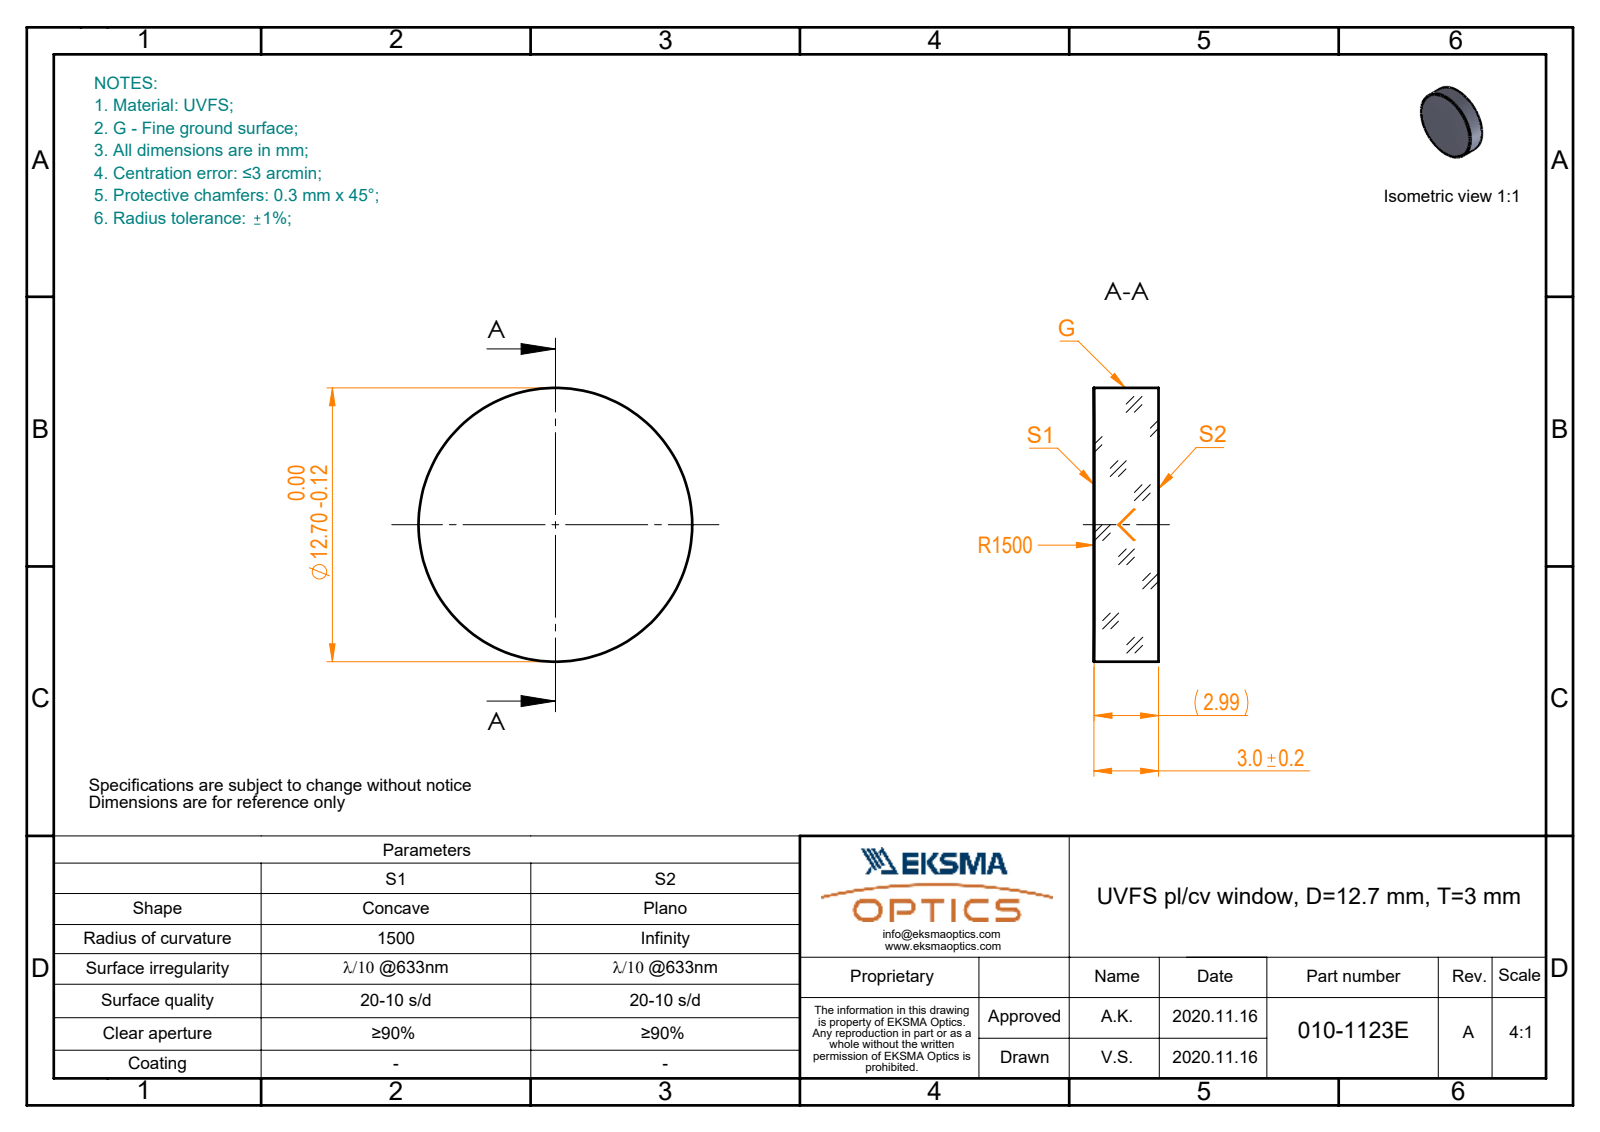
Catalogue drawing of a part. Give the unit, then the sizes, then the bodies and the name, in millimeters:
Units: millimetres
Overall size (bounding box): 12.7 × 12.7 × 3
Round bosses / shafts (diameter × count): ⌀12.7 ×1
Volume: 379 mm³ · Surface area: 373 mm²
Bodies: 1 solid, 5 faces (1 planar, 2 cylindrical, 2 other)
Part name (STEP PRODUCT): 010-1123E_UVFS_PCV_window
STEP written by: SolidWorks 2019 (CONFIG_CONTROL_DESIGN)
